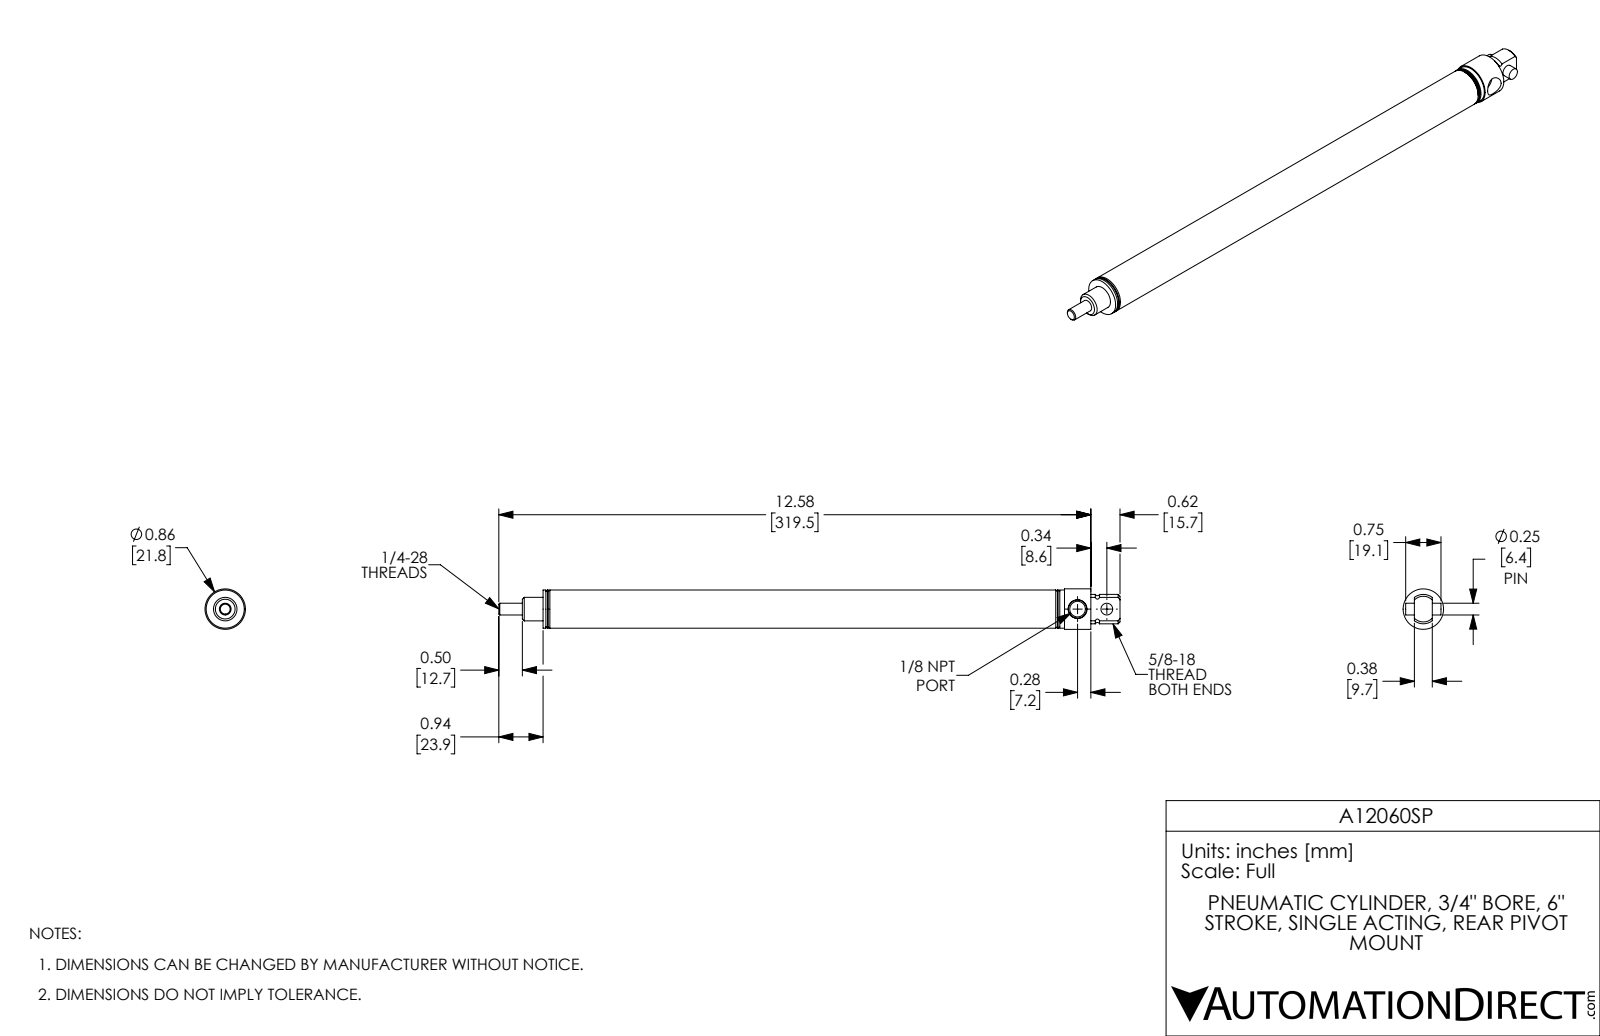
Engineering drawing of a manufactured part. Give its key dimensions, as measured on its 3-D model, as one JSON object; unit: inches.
{"part_name": "A12060SP-MainBody; A12060SP-Rod; A12060SP-Pin; A12060SP", "step_written_by": "SolidWorks 2017 (AUTOMOTIVE_DESIGN)", "units": "inches", "bodies": {"solids": 3, "faces": 73, "planar": 19, "cylindrical": 32, "other": 22}, "overall_size": [13.2, 0.86, 0.86], "volume_in3": 3.885, "surface_area_in2": 62.47, "round_holes": [[0.25, 2], [0.332, 1], [0.75, 1]], "round_bosses_or_shafts": [[0.86, 1], [0.81, 1], [0.5, 1]], "partial_cylinders_radius": [[0.313, 1]], "face_to_face_distances": [0.5, 6.5, 6, 2.57, 3.07, 9.07, 11.64, 9.07, 8.57, 2.57], "hole_center_spacings": [0.622]}
